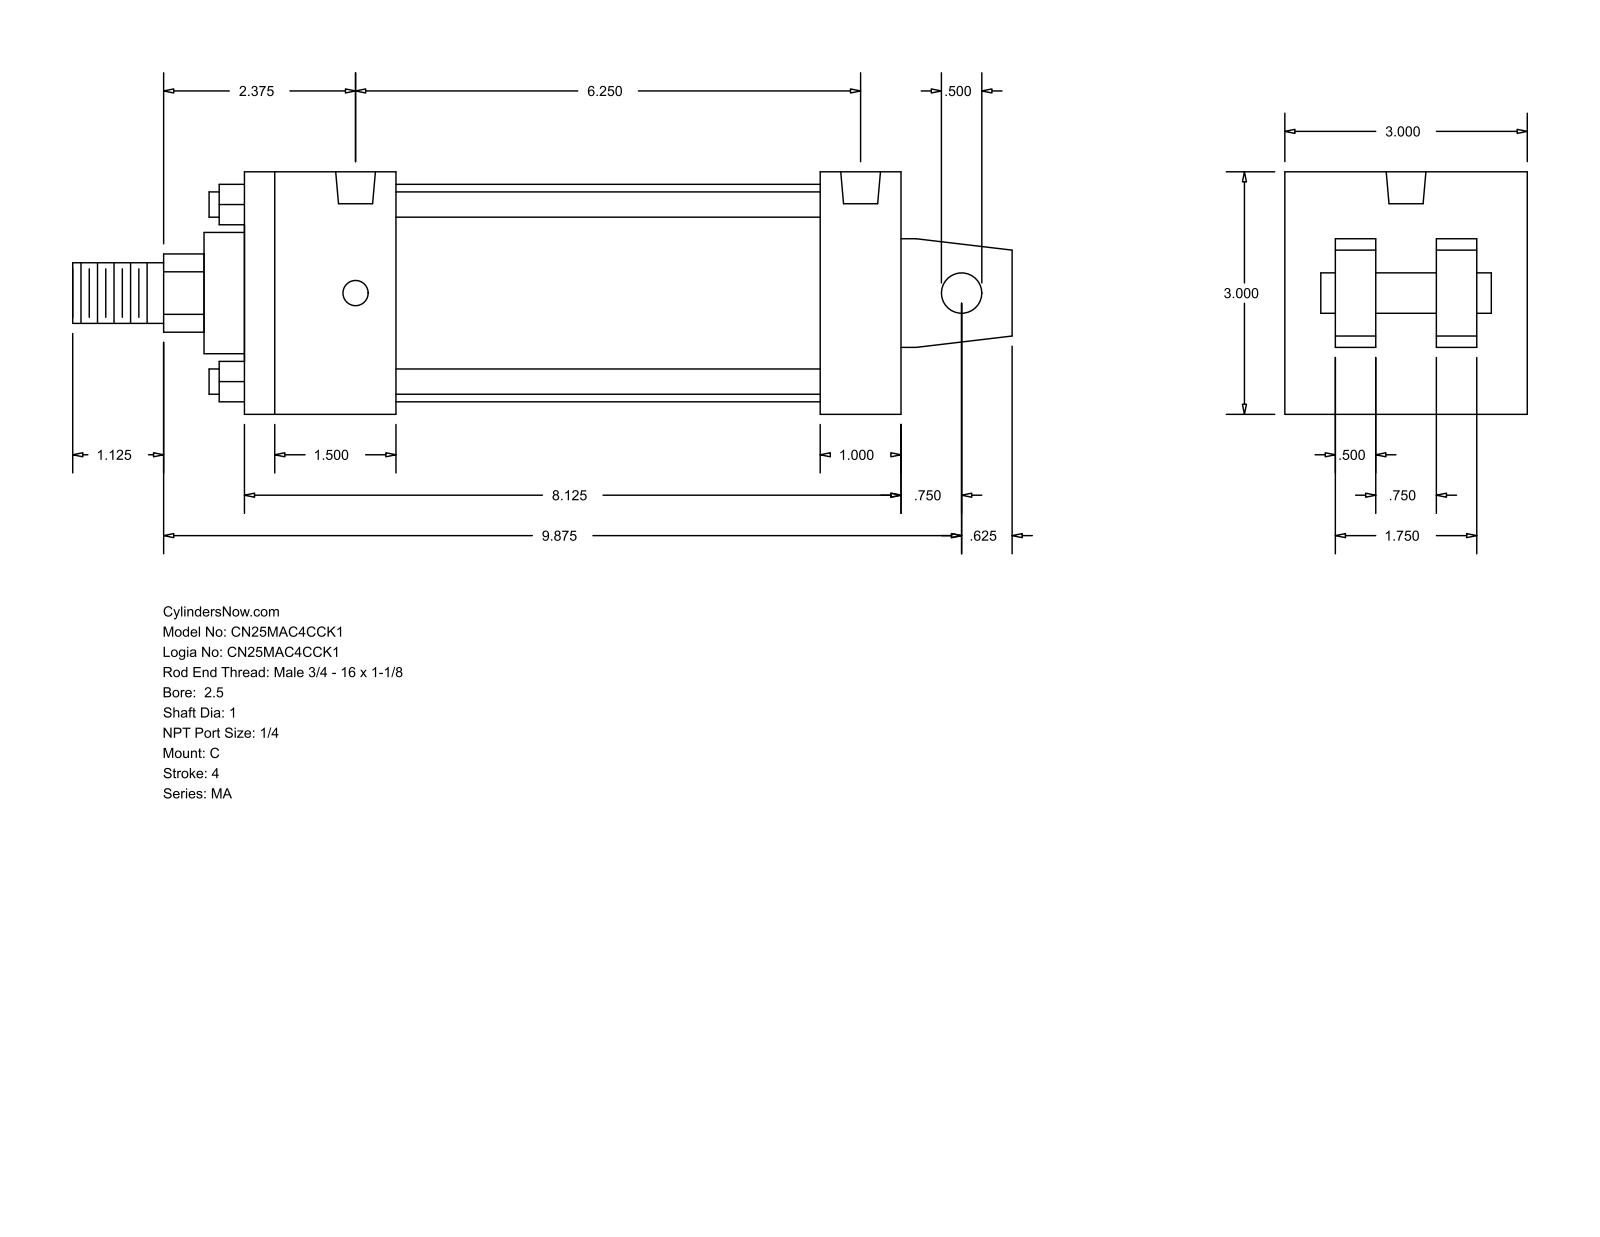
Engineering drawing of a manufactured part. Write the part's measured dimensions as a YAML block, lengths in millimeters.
part_name: "MA_C__0250_1"
step_written_by: "GSSL Pune (CONFIG_CONTROL_DESIGN)"
units: millimeters
bodies: {solids: 0, faces: 103, planar: 76, cylindrical: 27, other: 0}
overall_size: [295.27, 76.2, 76.2]
round_holes:
  - {diameter: 7.94, count: 4}
  - {diameter: 12.49, count: 2}
round_bosses_or_shafts:
  - {diameter: 7.94, count: 4}
  - {diameter: 68.33, count: 1}
  - {diameter: 38.1, count: 1}
  - {diameter: 25.4, count: 1}
  - {diameter: 19.05, count: 1}
  - {diameter: 12.7, count: 1}
partial_cylinders:
  - {radius: 12.29, count: 1}
face_to_face_distances: [76.2, 206.38, 47.63, 12.7, 60.33, 15.87, 25.4, 28.57, 180.98, 133.35]
hole_center_spacings: [158.74]
